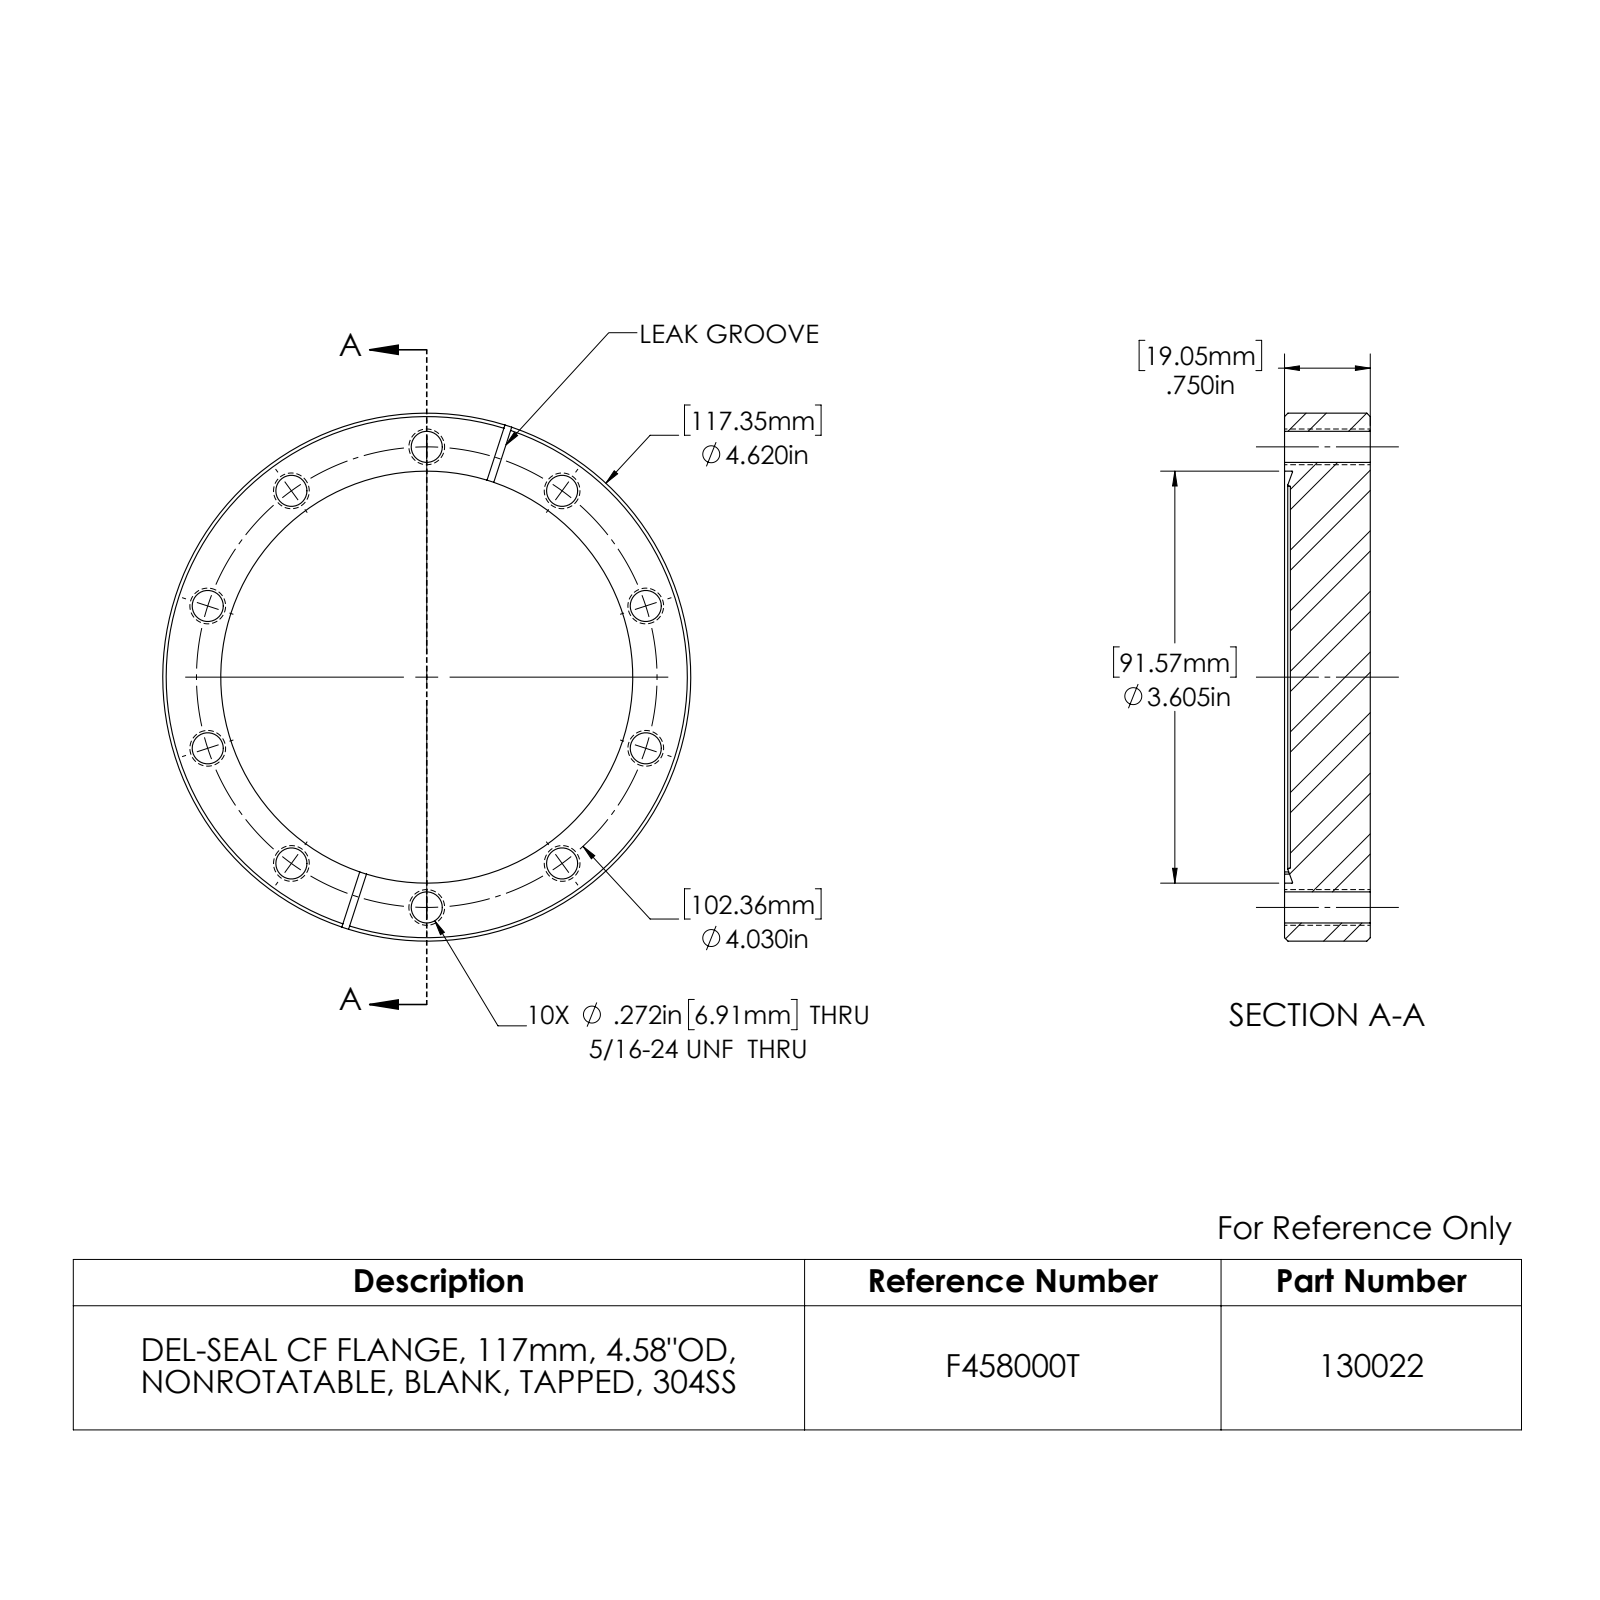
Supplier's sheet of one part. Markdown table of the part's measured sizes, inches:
| quantity | value |
| --- | --- |
| part name | 130022_E |
| STEP written by | SolidWorks 2022 (CONFIG_CONTROL_DESIGN) |
| units | inches |
| bodies | 1 solid, 49 faces (10 planar, 24 cylindrical, 15 other) |
| overall size | 4.62 × 4.62 × 0.75 |
| volume | 11.6 in³ |
| surface area | 50.27 in² |
| round holes (diameter × count) | 0.272 × 10, 3.605 × 1 |
| round bosses / shafts (diameter × count) | 4.62 × 1 |
| main face-to-face distances | 0.699, 0.051, 0.75, 0.052, 0.698, 0.062 |
| hole center spacings | 1.246, 2.015, 3.261, 3.833, 1.245, 2.015, 2.369, 2.369 |
